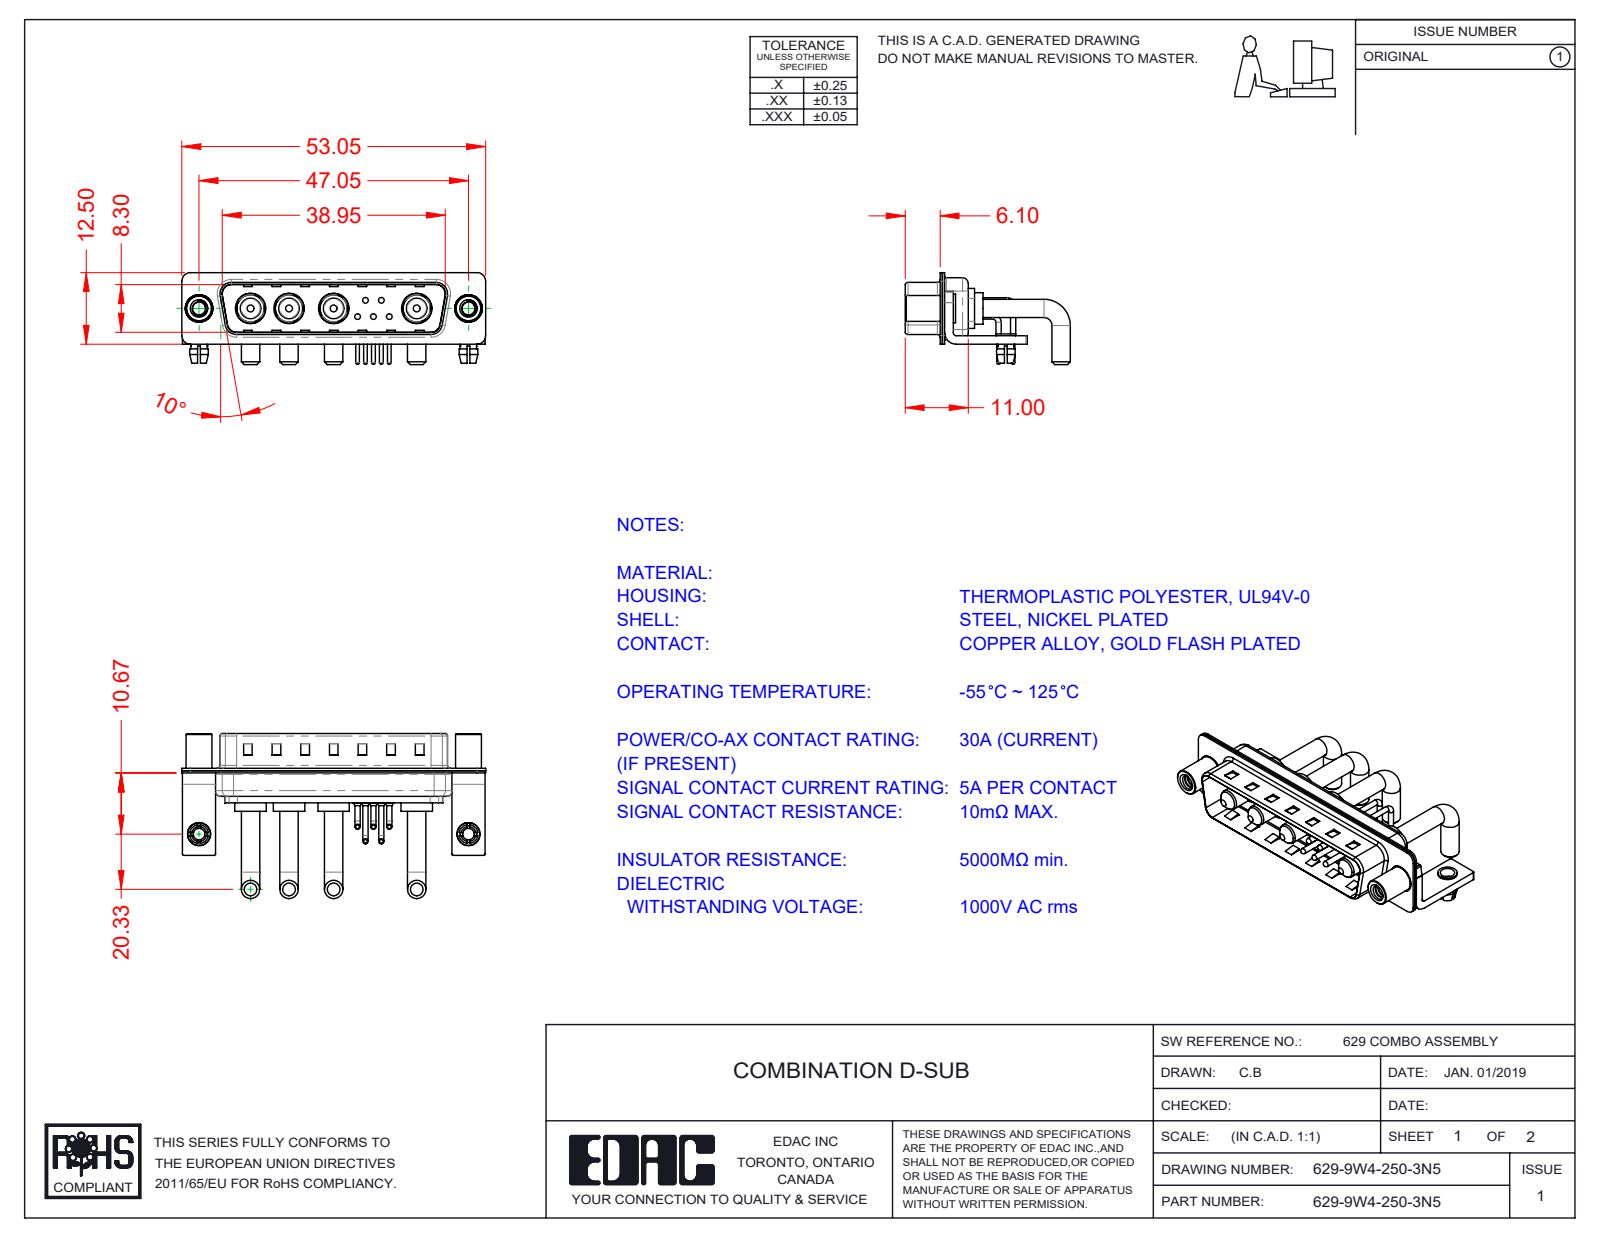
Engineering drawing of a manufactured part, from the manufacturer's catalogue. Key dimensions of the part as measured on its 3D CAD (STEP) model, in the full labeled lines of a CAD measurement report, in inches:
Part name (STEP PRODUCT): 629Combo Shell Rear_25 Contacts; 629Combo Housing_9W4; 629-9W4-250-3N5; 629Combo Shell Front_25 Contacts (+6 more)
STEP written by: SolidWorks 2020 (CONFIG_CONTROL_DESIGN)
Units: inches
Bodies: 22 solids, 1278 faces (601 planar, 493 cylindrical, 184 other)
Overall size (bounding box): 2.089 × 1.135 × 0.632
Volume: 0.249 in³ · Surface area: 13.54 in²
Round holes (diameter × count): ⌀0.079 ×7, ⌀0.03 ×5, ⌀0.063 ×5, ⌀0.191 ×4, ⌀0.209 ×4, ⌀0.089 ×2, ⌀0.098 ×2, ⌀0.126 ×2, ⌀0.157 ×2, ⌀0.189 ×2
Round bosses / shafts (diameter × count): ⌀0.035 ×10, ⌀0.126 ×8, ⌀0.059 ×5, ⌀0.039 ×5, ⌀0.026 ×5, ⌀0.217 ×4, ⌀0.205 ×4, ⌀0.187 ×4
Partial cylindrical surfaces — rounded edges, fillets, slot ends (radius × count): R0.01 ×16, R0.059 ×16, R0.079 ×13, R0.02 ×9, R0.063 ×8, R0.04 ×5, R0.024 ×4, R0.026 ×4
Main face-to-face distances: 0.016, 0.031, 0.374, 0.059, 0.358, 0.343, 0.39, 0.205, 0.03, 0.047
Hole centre spacings: 0.124, 0.109, 0.198, 0.571, 1.852, 0.109, 0.173, 0.174
